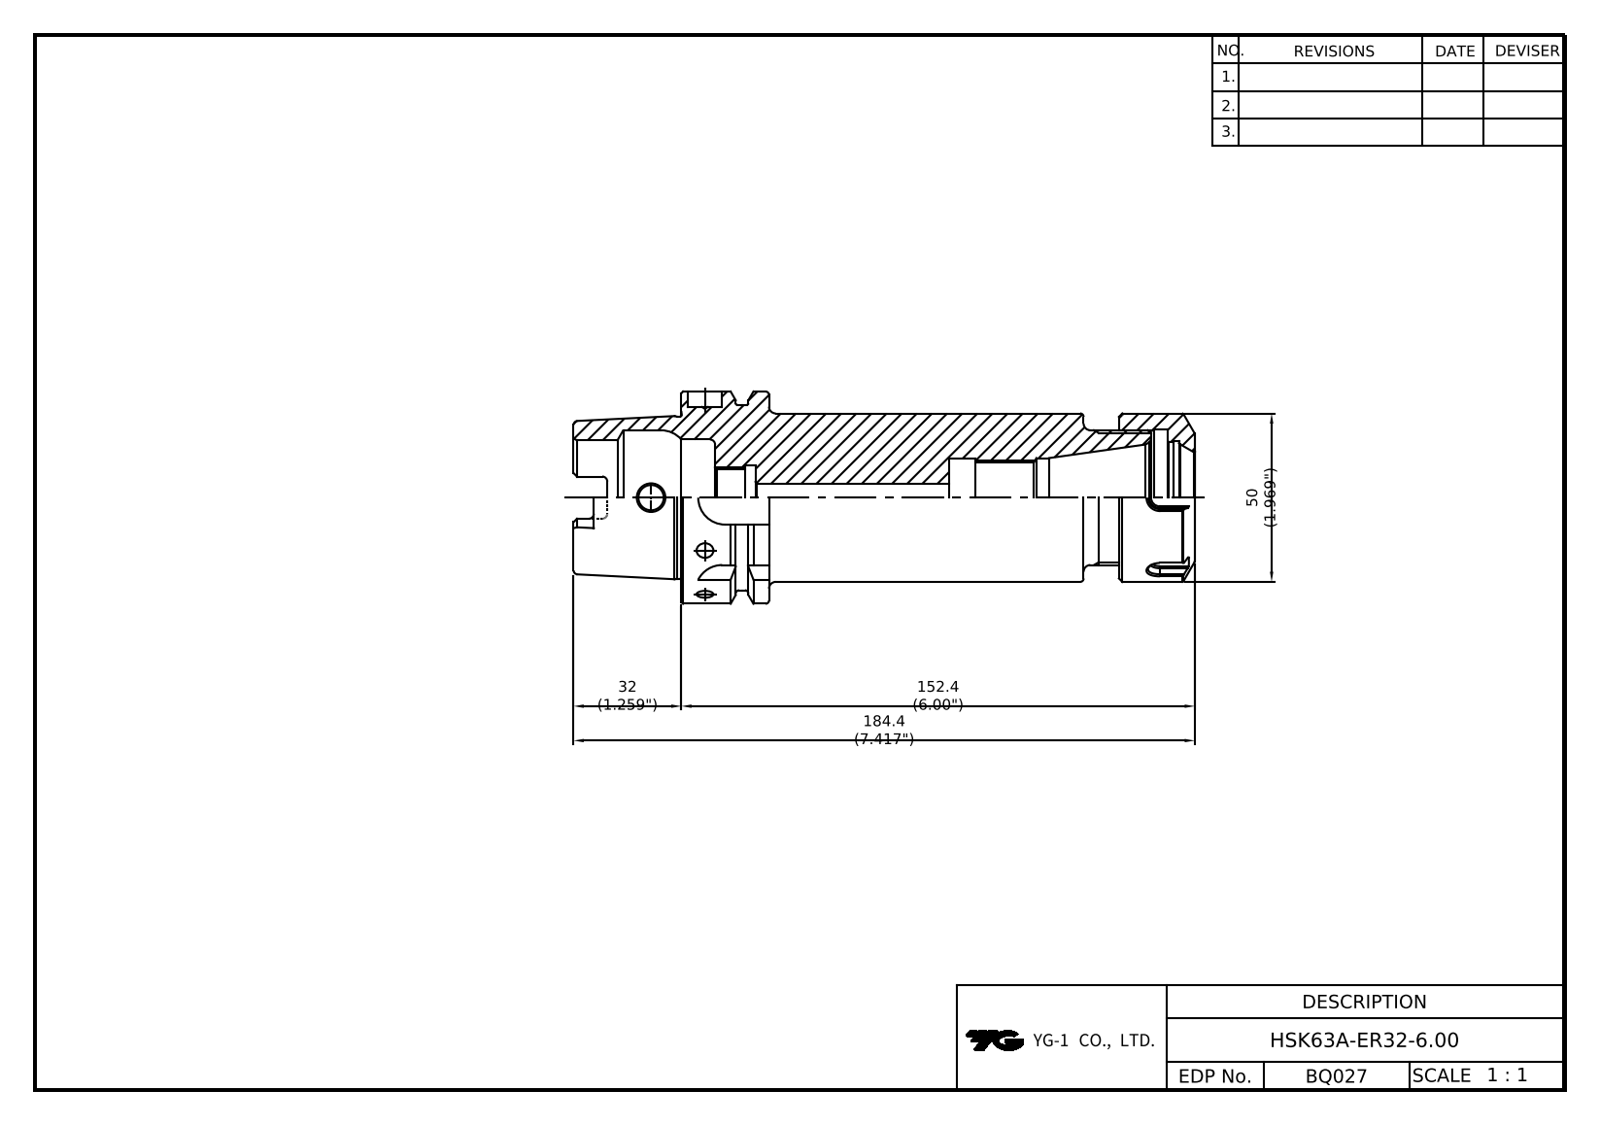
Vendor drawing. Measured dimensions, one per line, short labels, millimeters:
name: LO-HSK63A-ER32-212.4; ER32NUT
written by: Autodesk Inventor 2025 (AP242_MANAGED_MODEL_BASED_3D_ENGINEERING_MIM_LF)
unit: mm
bodies: 2 solids, 205 faces (80 planar, 54 cylindrical, 71 other)
size: 244.4 × 63 × 63
volume: 390 810 mm³; area: 64 620 mm²
holes: 1× ⌀1, 1× ⌀7.5, 1× ⌀8, 1× ⌀10, 1× ⌀16.92, 1× ⌀19, 1× ⌀20.5, 1× ⌀23, 1× ⌀23.5, 1× ⌀27.1, 1× ⌀31.4, 1× ⌀33.8
bosses: 1× ⌀63, 1× ⌀55, 1× ⌀50, 1× ⌀48.04
rounds: 12× R0.5, 6× R1.5, 4× R2.88, 4× R8
face distances: 26, 10, 16, 212.4, 186.4, 202.4, 189.9, 179.9, 163.9, 22.5
hole spacings: 0.8, 22, 22.8
